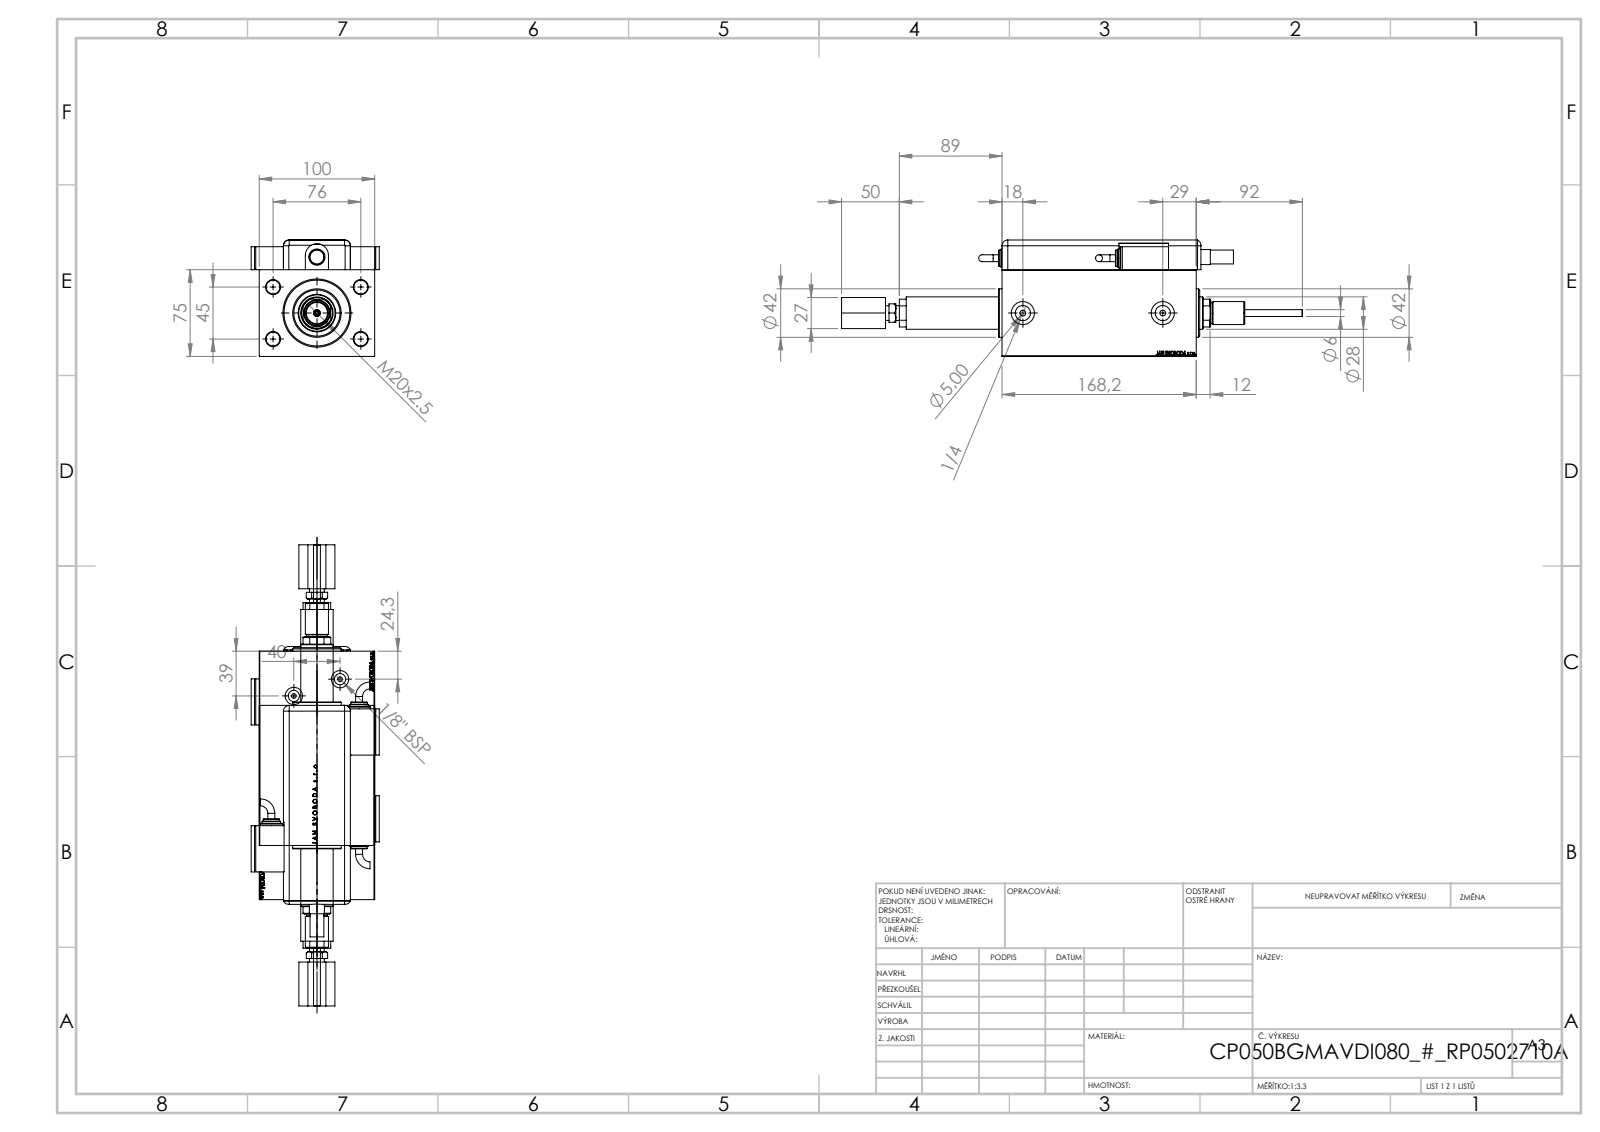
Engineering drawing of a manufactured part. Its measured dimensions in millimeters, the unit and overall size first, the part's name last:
Units: millimetres
Overall size (bounding box): 399.2 × 111 × 100.8
Round holes (diameter × count): ⌀4 ×4, ⌀12 ×4, ⌀5 ×2, ⌀8 ×2, ⌀9.73 ×2, ⌀13.16 ×2, ⌀15 ×2, ⌀20 ×2, ⌀3 ×1, ⌀6 ×1, ⌀14 ×1, ⌀18.5 ×1
Round bosses / shafts (diameter × count): ⌀20 ×3, ⌀16 ×2, ⌀14 ×2, ⌀6 ×2, ⌀42 ×1, ⌀18 ×1, ⌀13 ×1, ⌀12.78 ×1
Partial cylindrical surfaces — rounded edges, fillets, slot ends (radius × count): R5 ×9, R10 ×1, R13.5 ×1
Main face-to-face distances: 75, 3, 100, 100.8, 25.8, 168.2, 24, 1, 97.8, 22.8
Hole centre spacings: 44.16, 45, 46.04, 76, 80.53, 88.32, 20, 20.42
Volume: 1 379 000 mm³ · Surface area: 236 465 mm²
Bodies: 11 solids, 1322 faces (618 planar, 141 cylindrical, 563 other)
Part name (STEP PRODUCT): SWITCH Q; KRYT; V450DCP_VC_B; SWITCH_Q_FRONT_BACK (+6 more)
STEP written by: SolidWorks 2019 (CONFIG_CONTROL_DESIGN)
